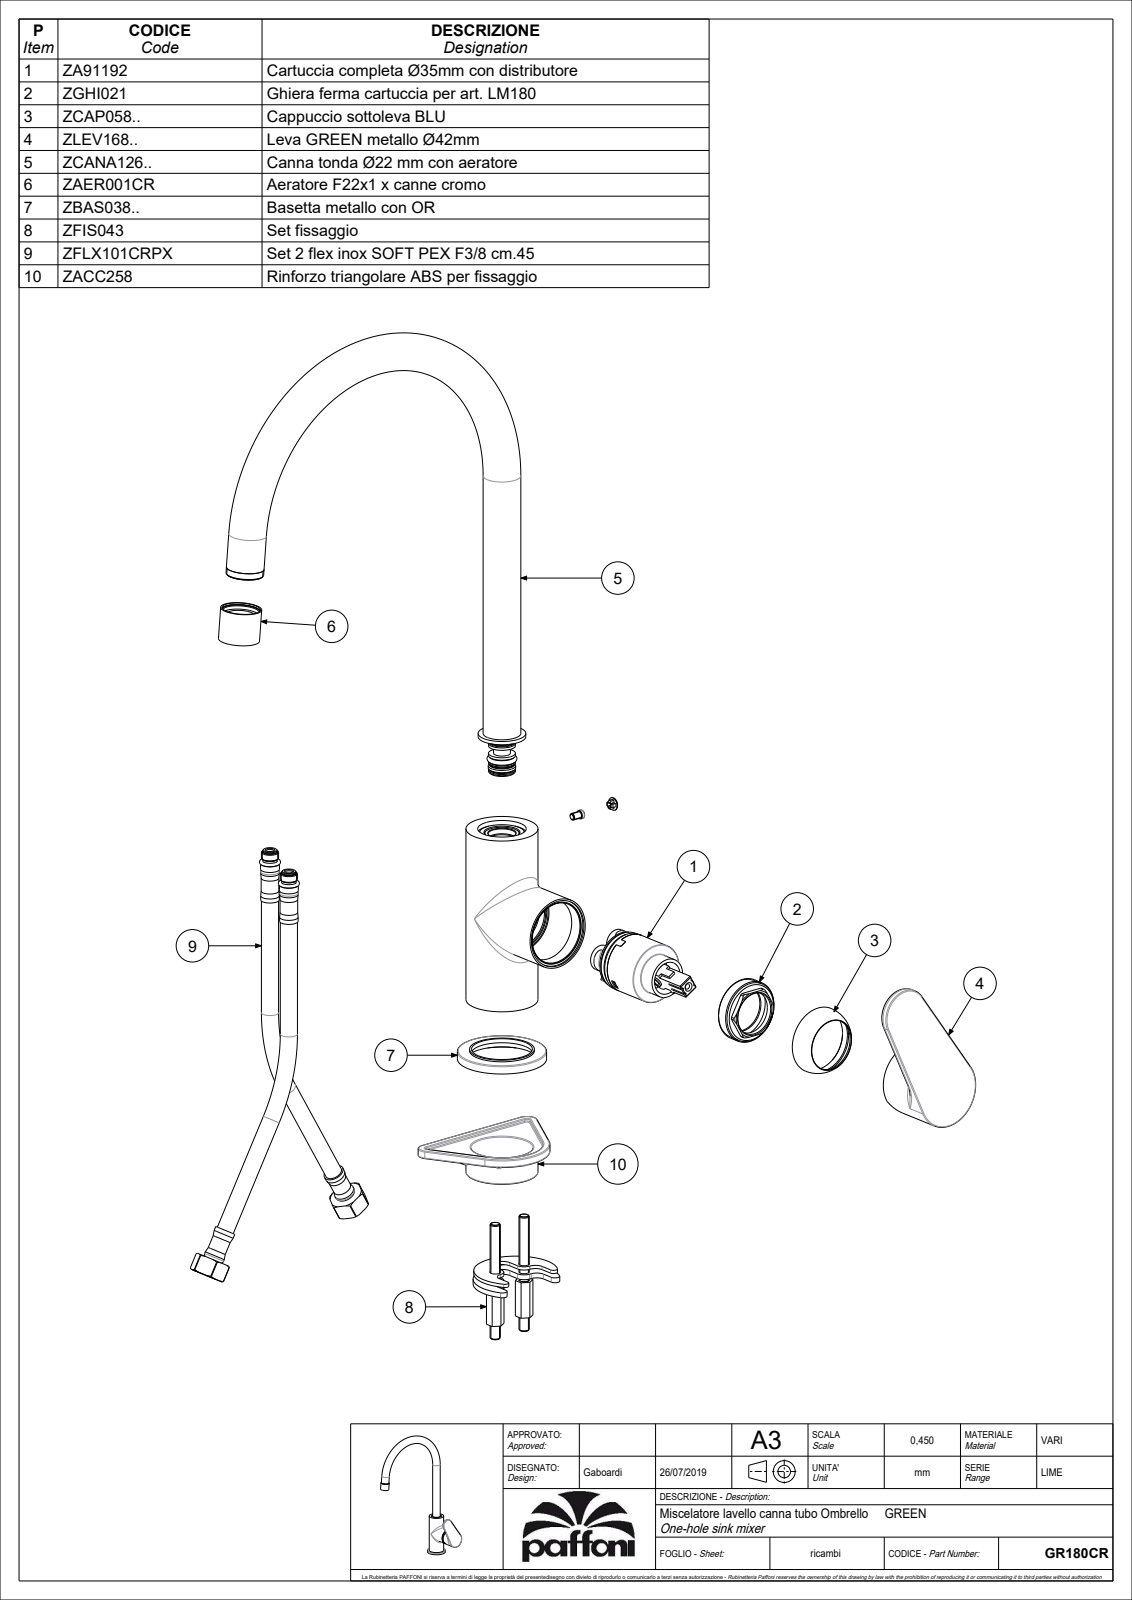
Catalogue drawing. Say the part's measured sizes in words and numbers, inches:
The part is named "GR180CR". Its 3-D file was written by "CREO PARAMETRIC BY PTC INC, 2020044 (CONFIG_CONTROL_DESIGN)". It is 4 solids with 2454 faces: 1872 planar, 359 cylindrical and 223 other. Overall it measures 14.921 by 11.712 by 2.883 inches. Its volume is 9.425 cubic inches and its surface area 244.6 square inches. Round holes: 3 of diameter 0.217, 3 of diameter 0.354, 3 of diameter 0.472, 2 of diameter 0.118, 2 of diameter 0.276, 2 of diameter 0.315, 2 of diameter 0.374, 2 of diameter 0.433, 2 of diameter 0.63, 2 of diameter 0.772, 2 of diameter 1.496, 2 of diameter 1.535. Round bosses or shafts: 3 of diameter 1.654, 2 of diameter 0.866, 2 of diameter 0.299, 2 of diameter 0.157, 1 of diameter 2.047, 1 of diameter 1.677, 1 of diameter 1.488, 1 of diameter 1.457. Partial cylindrical surfaces (rounded edges, fillets, slot ends): 64 of radius 0.02, 21 of radius 0.012, 6 of radius 0.039, 4 of radius 0.177, 3 of radius 0.285, 2 of radius 0.008, 2 of radius 0.118, 2 of radius 0.197. The main face-to-face distances are 0.079, 0.098, 1.339, 0.138, 1.417, 0.236, 1.398, 2.756, 0.02, 0.197. The hole center spacings are 0.513, 0.028, 0.335, 0.336, 0.339, 0.366, 0.511, 0.52.
